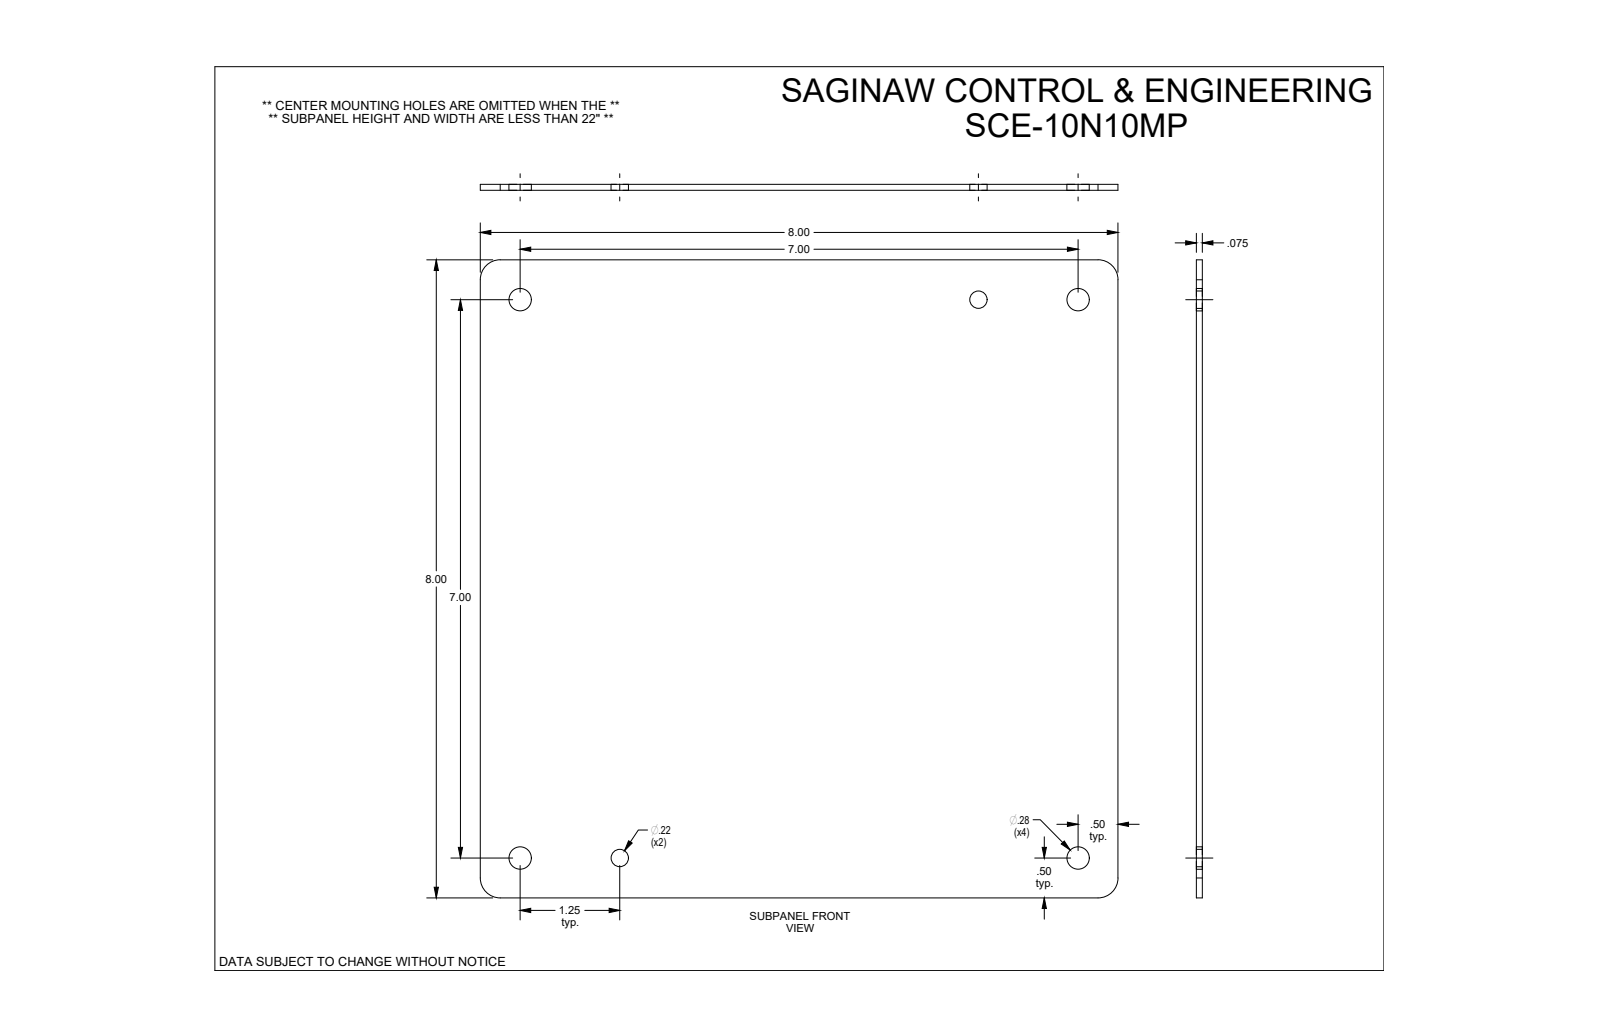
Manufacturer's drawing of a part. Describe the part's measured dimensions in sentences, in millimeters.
The part is named "SCE-10N10MP". Its 3-D file was written by "SolidWorks 2019 (CONFIG_CONTROL_DESIGN)". It is 1 solid with 16 faces: 6 planar, 10 cylindrical and 0 other. Overall it measures 203.2 by 203.2 by 1.9 millimeters. Its volume is 78 200 cubic millimeters and its surface area 83 870 square millimeters. Round holes: 4 of diameter 7.1, 2 of diameter 5.5. Partial cylindrical surfaces (rounded edges, fillets, slot ends): 4 of radius 6.4. The main face-to-face distances are 1.9, 203.2. The hole center spacings are 177.8, 31.8, 146.1, 180.6, 230.1, 251.5, 211.4.
